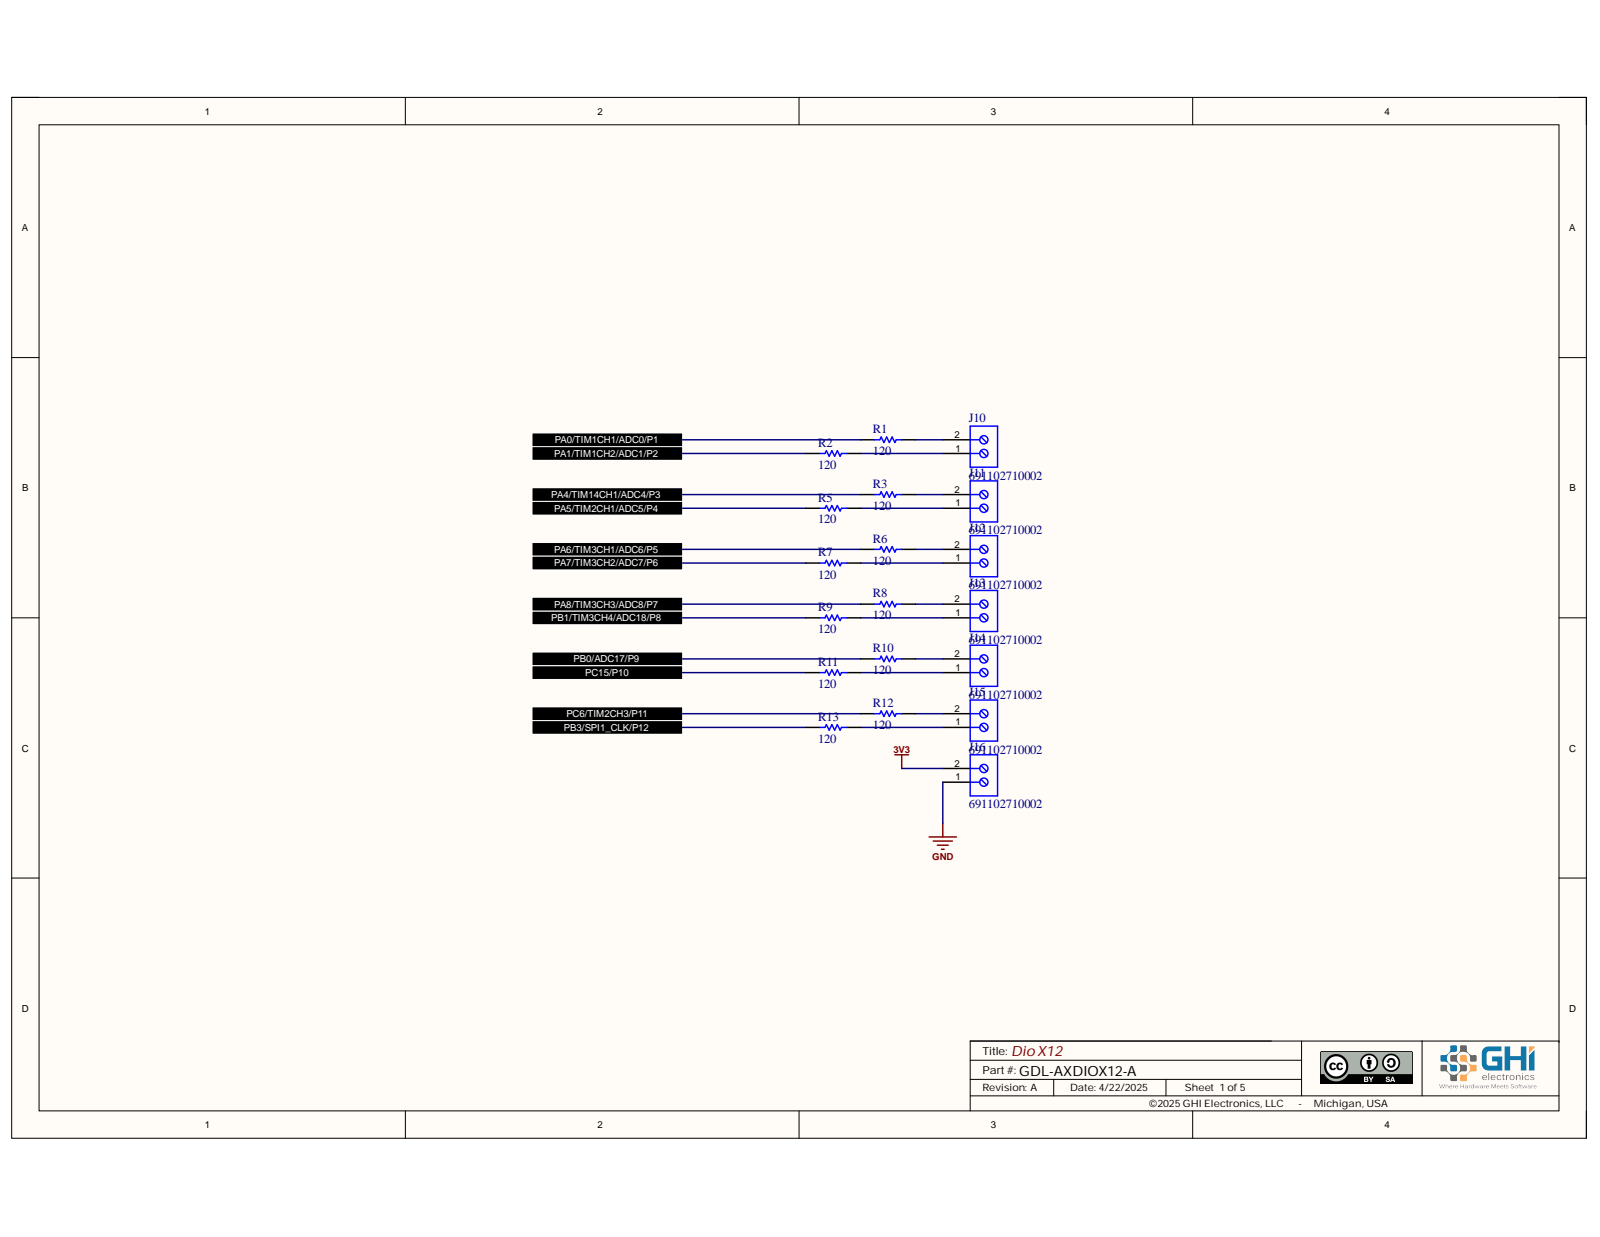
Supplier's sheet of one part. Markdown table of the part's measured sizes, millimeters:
| quantity | value |
| --- | --- |
| part name | PCB; Board; R13; 5251392352 (+7 more) |
| STEP written by | Open CASCADE 7.5 (AUTOMOTIVE_DESIGN) |
| units | millimeters |
| bodies | 164 solids, 2900 faces (2162 planar, 540 cylindrical, 198 other) |
| overall size | 87 × 22 × 13.4 |
| volume | 4 186 mm³ |
| surface area | 13 893 mm² |
| round holes (diameter × count) | 3 × 18, 0.6 × 14, 1.3 × 14, 2 × 14, 2.75 × 14, 3.5 × 14, 1.02 × 2 |
| round bosses / shafts (diameter × count) | 2.5 × 14, 1 × 14 |
| partial cylindrical surfaces (radius × count) | 0.8 × 56, 0.12 × 35, 0.2 × 28, 0.15 × 14, 0.47 × 14, 3.5 × 4, 0.1 × 2, 0.17 × 2 |
| main face-to-face distances | 10, 5, 20, 5.5, 30, 1.11, 0.91, 0.85, 4, 50 |
| hole center spacings | 5, 10, 15, 20, 25, 30, 5.94, 35 |
